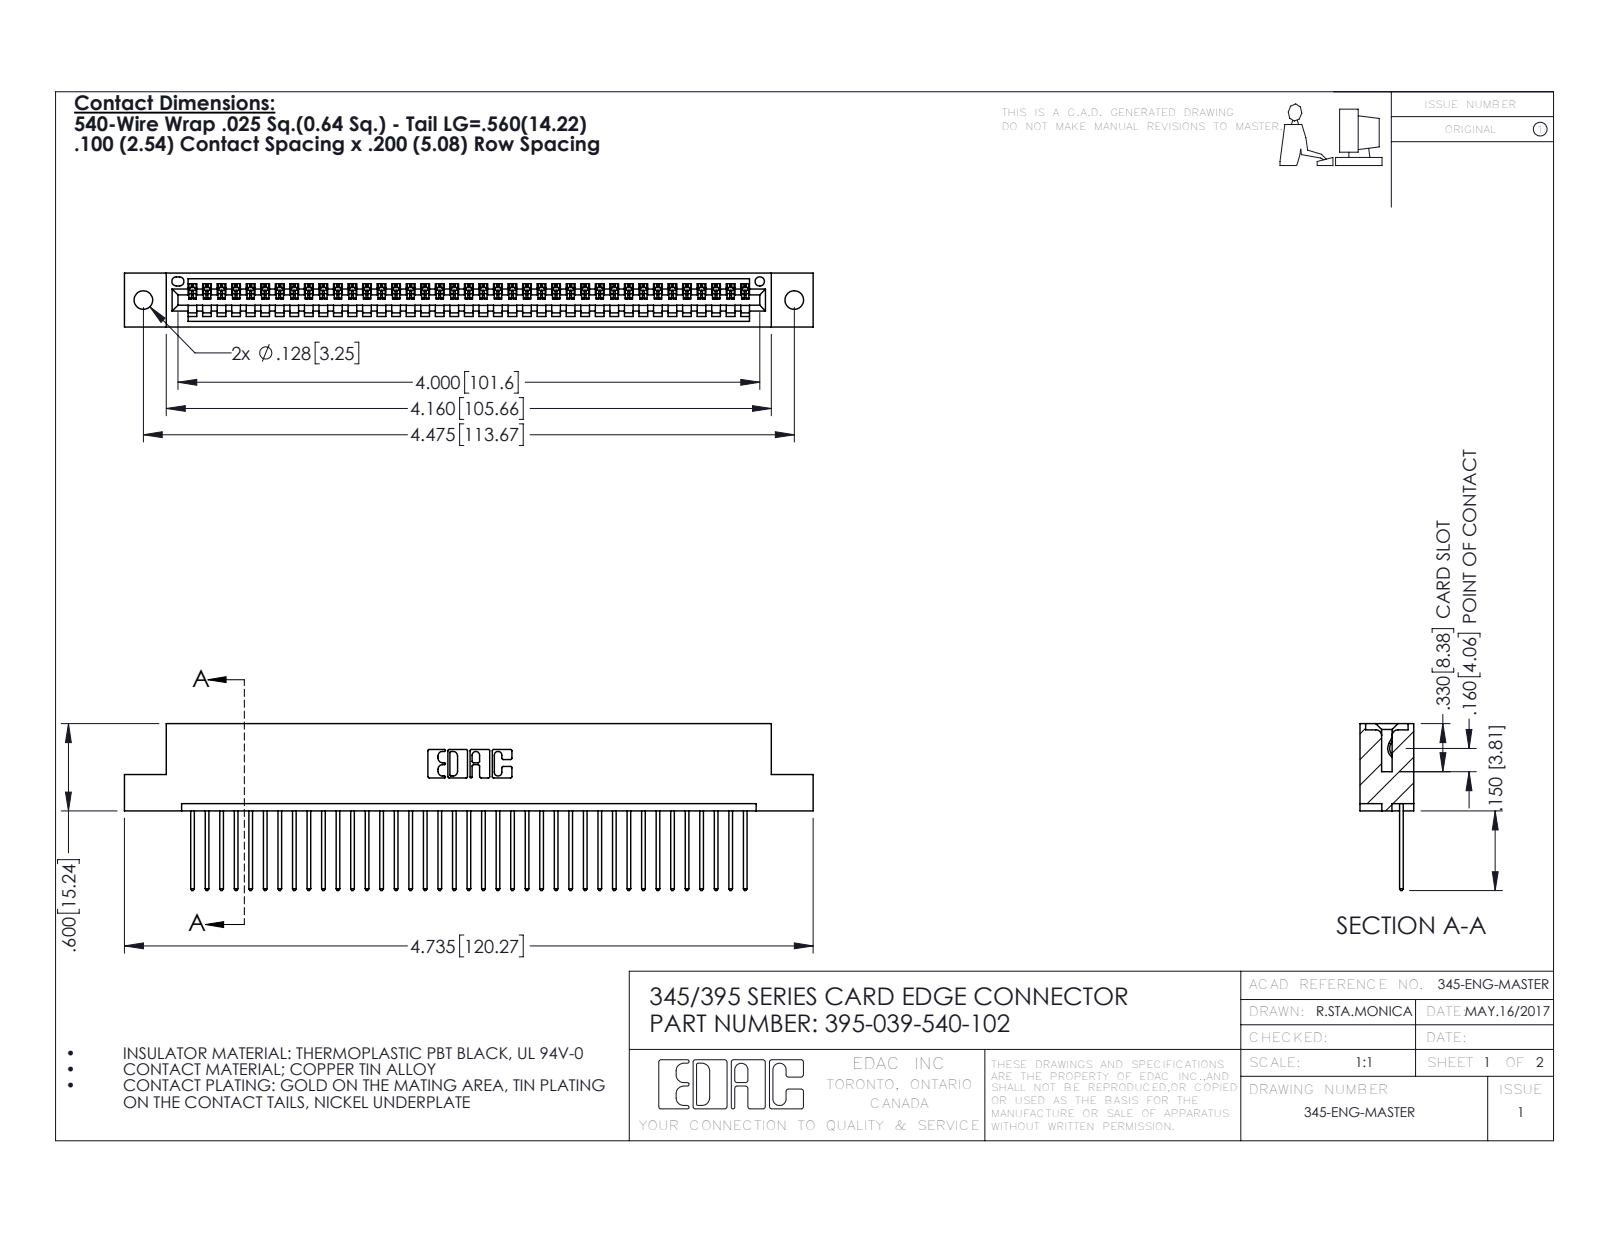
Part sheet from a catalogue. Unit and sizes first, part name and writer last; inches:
Units: inches
Overall size (bounding box): 4.735 × 1.147 × 0.37
Round holes (diameter × count): ⌀0.128 ×2, ⌀0.064 ×1
Partial cylindrical surfaces — rounded edges, fillets, slot ends (radius × count): R0.006 ×78, R0.01 ×78, R0.01 ×22, R0.007 ×6, R0.031 ×6, R0.026 ×3, R0.031 ×2, R0.04 ×2
Main face-to-face distances: 0.298, 0.072, 0.37, 0.2, 0.098, 0.272, 0.025, 0.225, 0.149, 0.072
Hole centre spacings: 0.27, 4.239, 4.475
Volume: 0.697 in³ · Surface area: 23.62 in²
Bodies: 40 solids, 2388 faces (1640 planar, 748 cylindrical, 0 other)
Part name (STEP PRODUCT): 345-292-001_345-293-140; 345 Part_Flush Mounting Lugs - 0.128 Dia; 395-039-540-102
STEP written by: SolidWorks 2016 (CONFIG_CONTROL_DESIGN)
